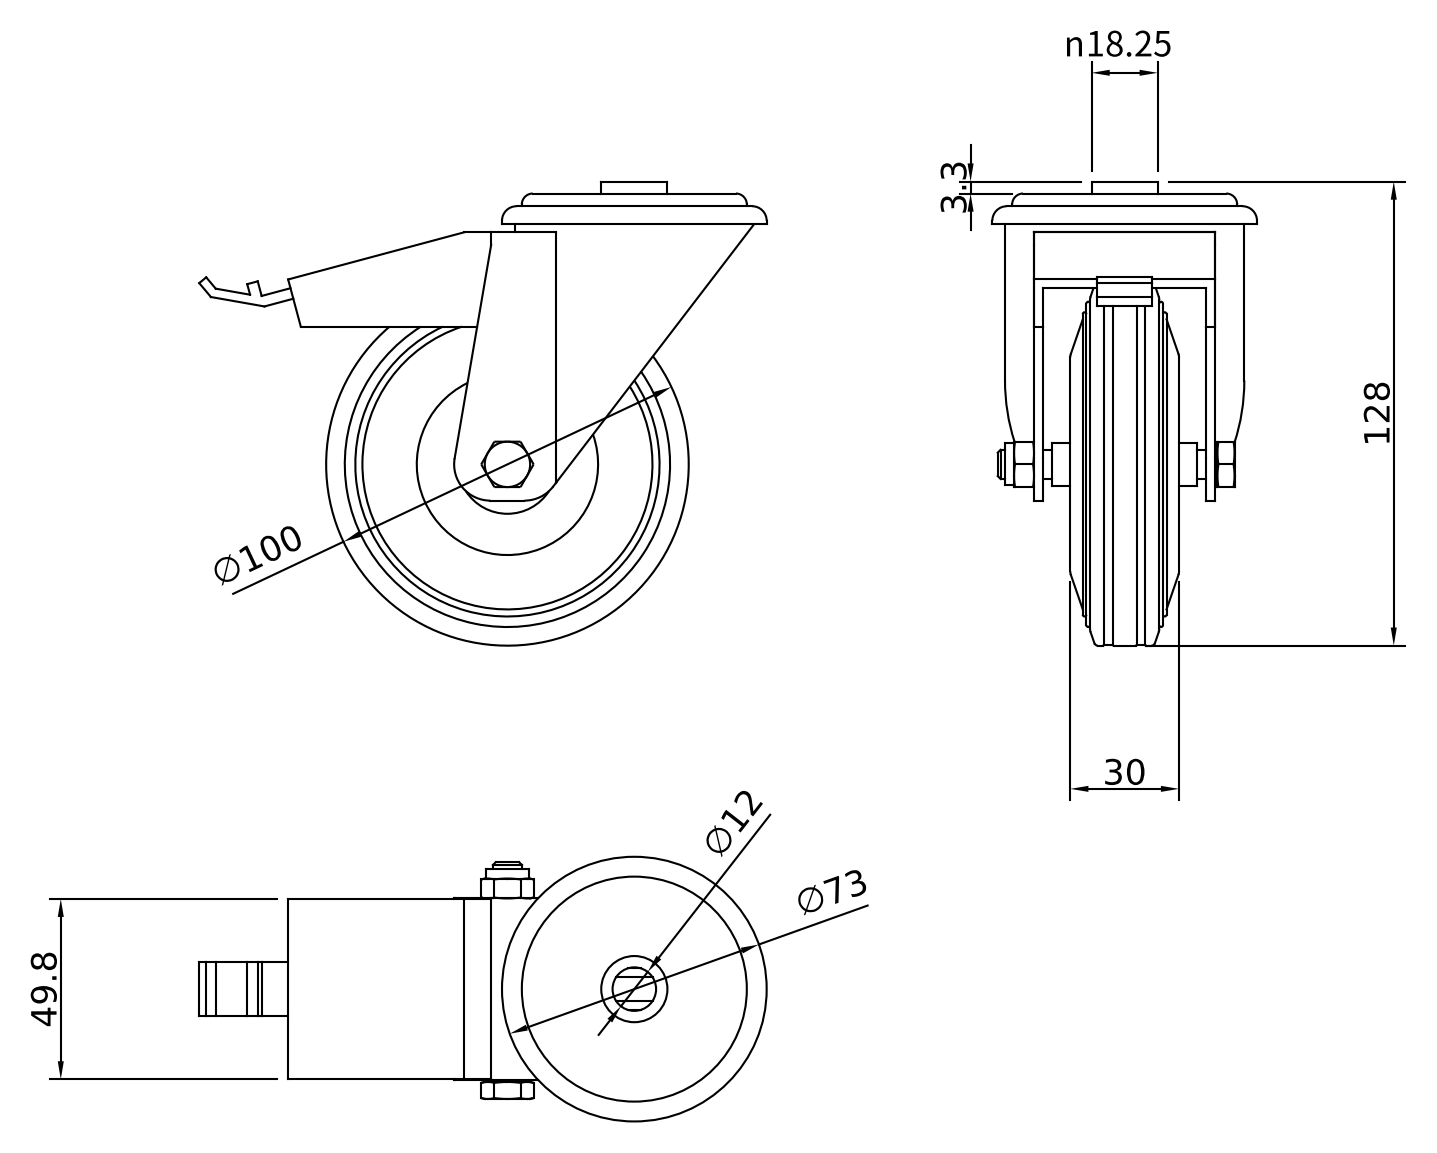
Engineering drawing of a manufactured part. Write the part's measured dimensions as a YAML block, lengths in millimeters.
part_name: "CRUST0000198; 440000025840; 440000025839; 440000025838"
step_written_by: "Autodesk Inventor 2022 (AUTOMOTIVE_DESIGN)"
units: millimeters
bodies: {solids: 3, faces: 151, planar: 73, cylindrical: 25, other: 53}
overall_size: [156.5, 128, 73]
volume: 254209
surface_area: 67587
round_holes:
  - {diameter: 12, count: 2}
  - {diameter: 61, count: 1}
round_bosses_or_shafts:
  - {diameter: 100, count: 1}
  - {diameter: 99.4, count: 1}
  - {diameter: 73, count: 1}
  - {diameter: 66, count: 1}
  - {diameter: 62.05, count: 1}
  - {diameter: 18.25, count: 1}
  - {diameter: 11.63, count: 1}
  - {diameter: 8, count: 1}
partial_cylinders:
  - {radius: 10, count: 2}
face_to_face_distances: [2.5, 47.5, 45, 10.7, 7.5, 40, 10, 37.5, 49.9, 2.4]
